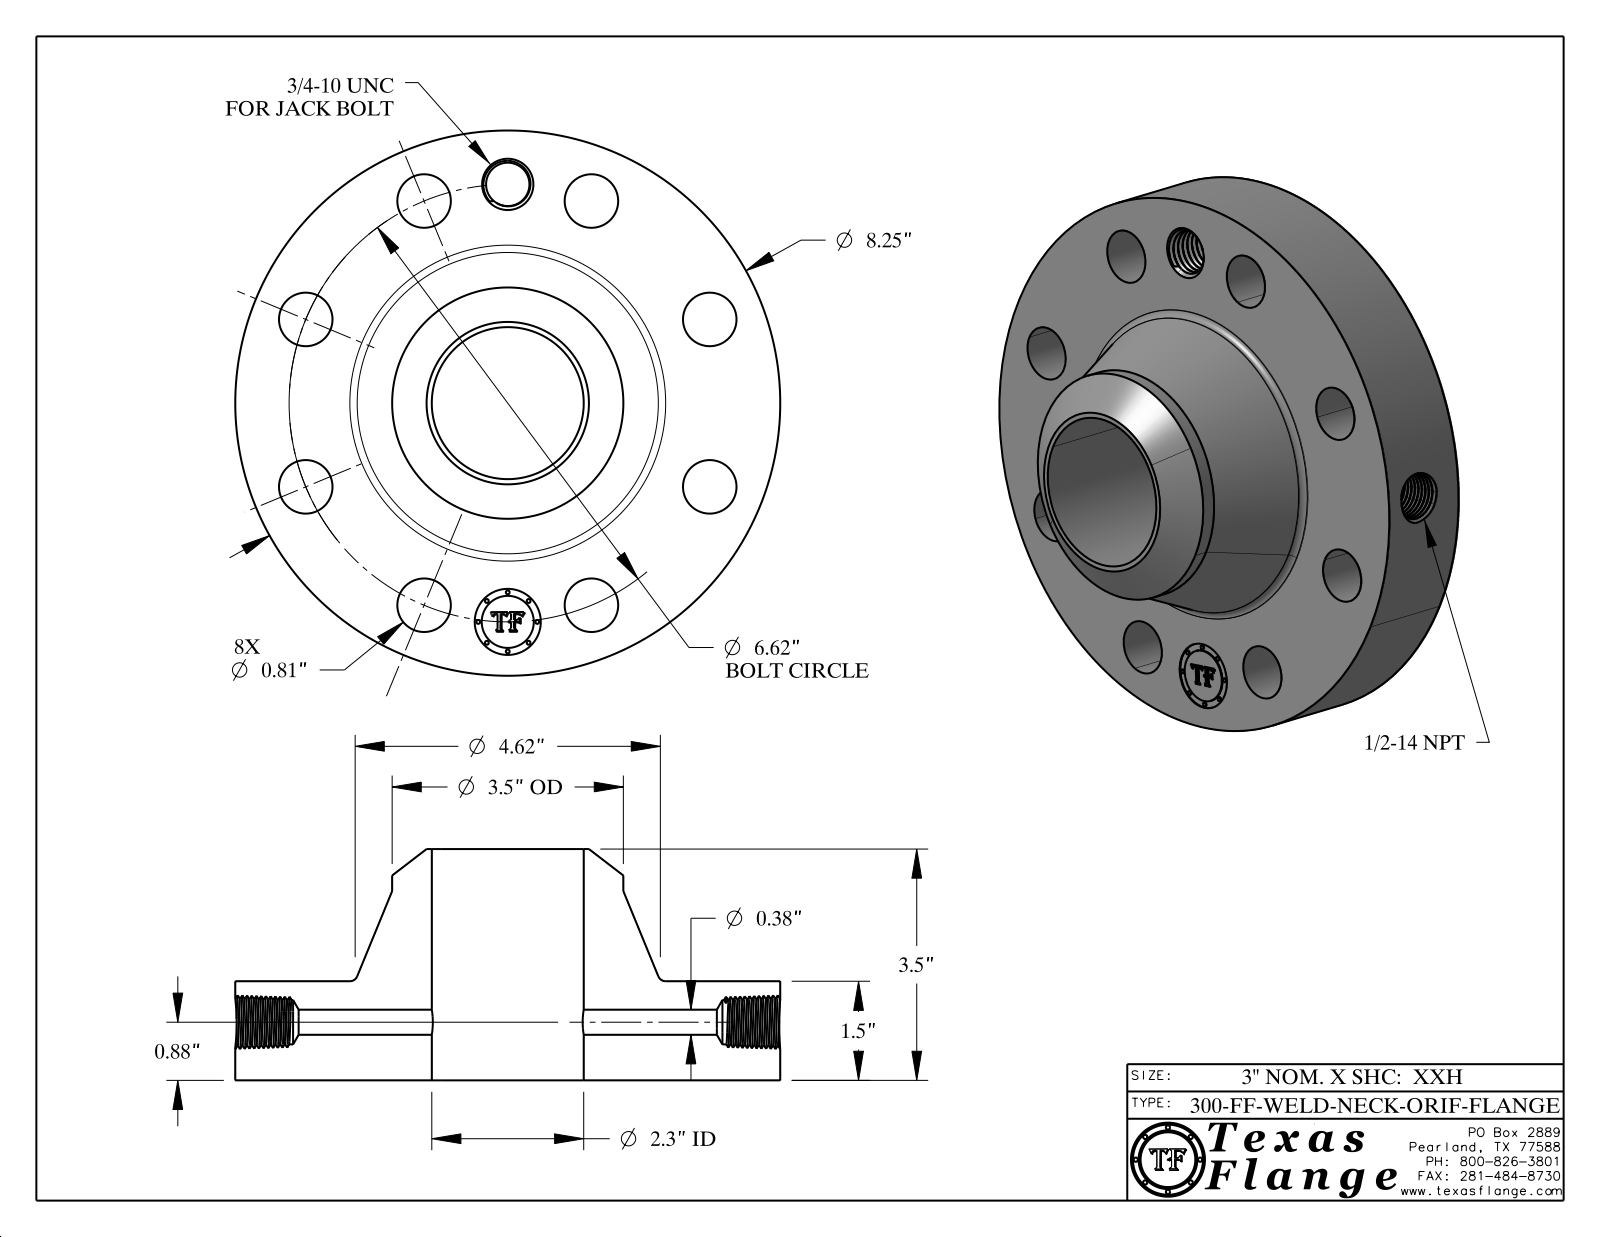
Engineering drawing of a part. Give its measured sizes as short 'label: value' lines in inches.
name: 300-FF-WELD-NECK
written by: CATIA V5 STEP AP214 (AUTOMOTIVE_DESIGN)
unit: in
bodies: 1 solid, 766 faces (368 planar, 90 cylindrical, 308 other)
size: 8.25 × 8.25 × 3.5
volume: 80.51 in³; area: 215.6 in²
holes: 8× ⌀0.81, 1× ⌀0.38, 1× ⌀0.656, 1× ⌀0.672, 1× ⌀1, 1× ⌀2.3
bosses: 8× ⌀0.061, 1× ⌀8.25, 1× ⌀3.5, 1× ⌀0.788
face distances: 1.5, 3.5, 2, 0.015, 1.485, 2.015, 0.298, 0.293, 0.054, 0.248
hole spacings: 3.31, 4.681, 6.116, 6.62, 1.291, 2.533, 2.533, 3.678
